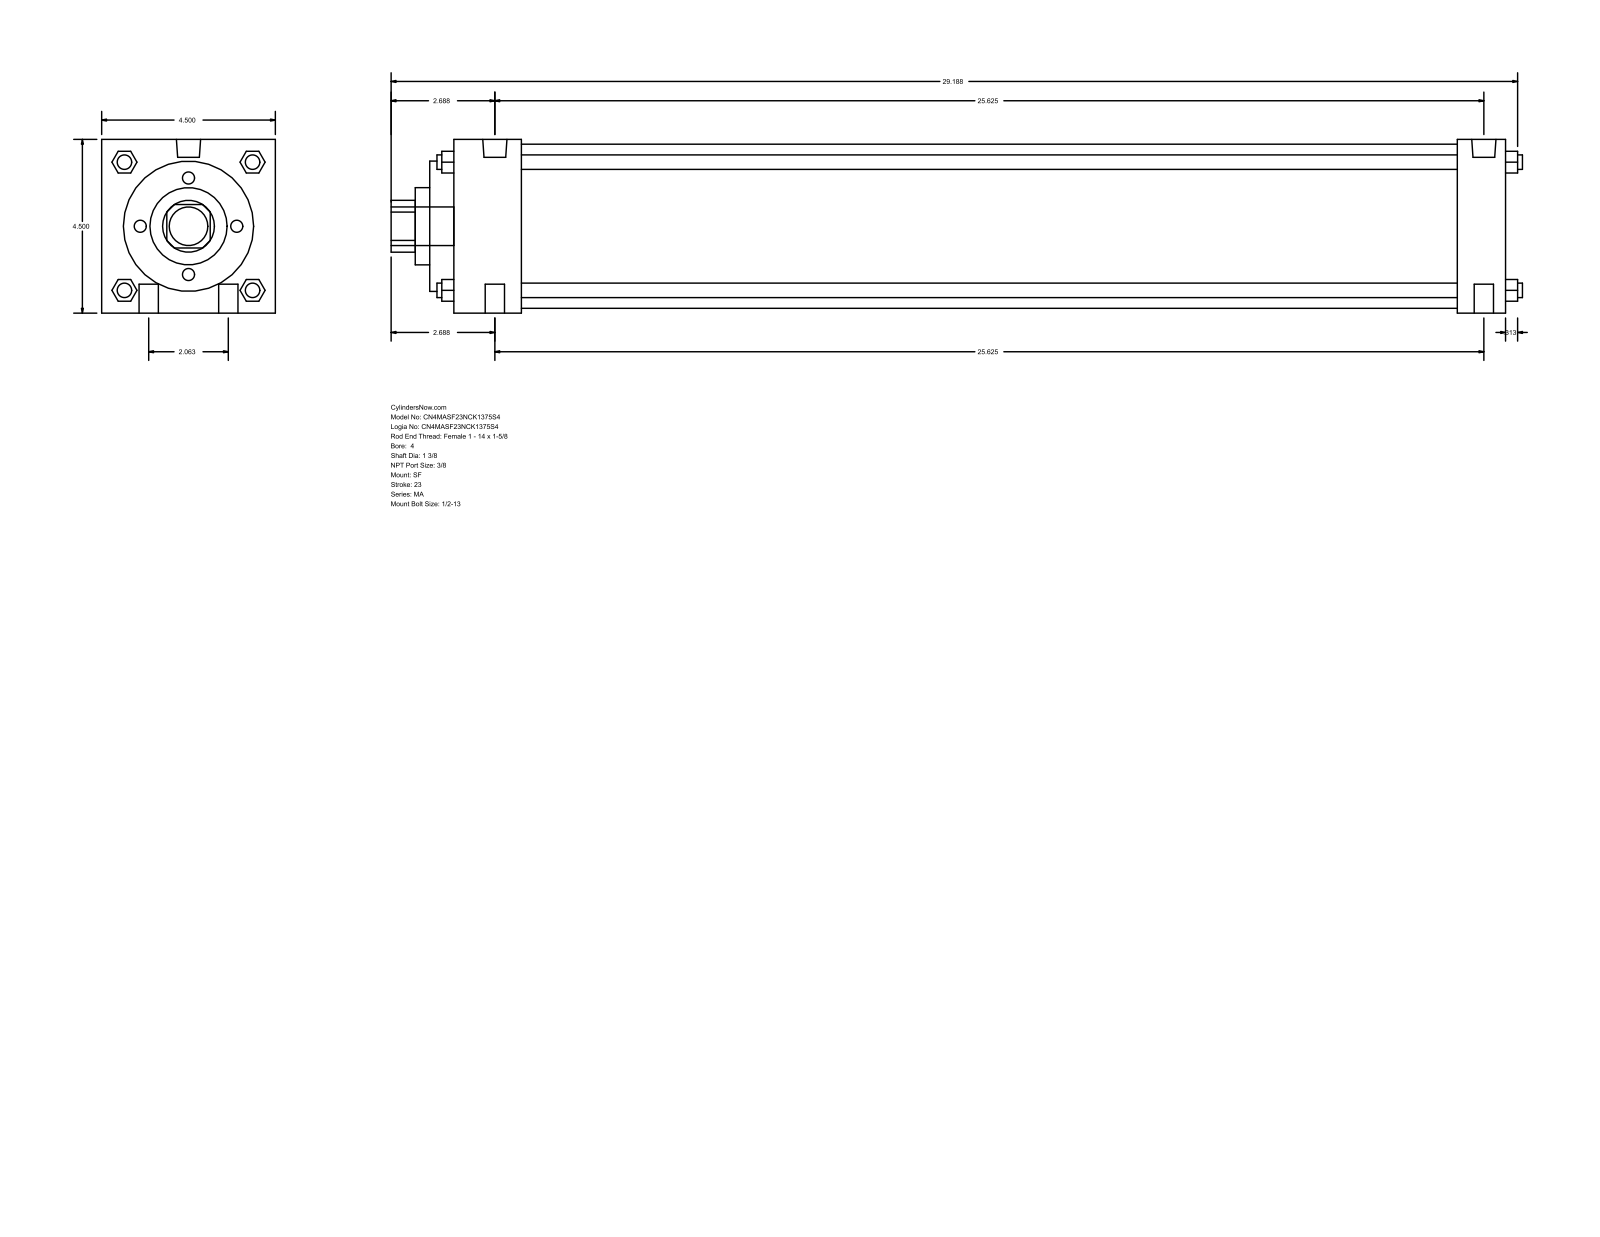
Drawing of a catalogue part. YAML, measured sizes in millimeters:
part_name: "MA_SF__0400_1.375"
step_written_by: "GSSL Pune (CONFIG_CONTROL_DESIGN)"
units: millimeters
bodies: {solids: 0, faces: 126, planar: 95, cylindrical: 31, other: 0}
overall_size: [744.54, 114.3, 114.3]
round_holes:
  - {diameter: 34.92, count: 1}
  - {diameter: 50.8, count: 1}
  - {diameter: 85.72, count: 1}
  - {diameter: 107.95, count: 1}
round_bosses_or_shafts:
  - {diameter: 12.7, count: 4}
  - {diameter: 9.53, count: 4}
  - {diameter: 15.93, count: 2}
  - {diameter: 11.11, count: 2}
  - {diameter: 25.4, count: 1}
partial_cylinders:
  - {radius: 17.06, count: 1}
face_to_face_distances: [114.3, 692.15, 708.02, 15.87, 676.27, 660.4, 31.75, 60.32, 44.45, 615.95]
